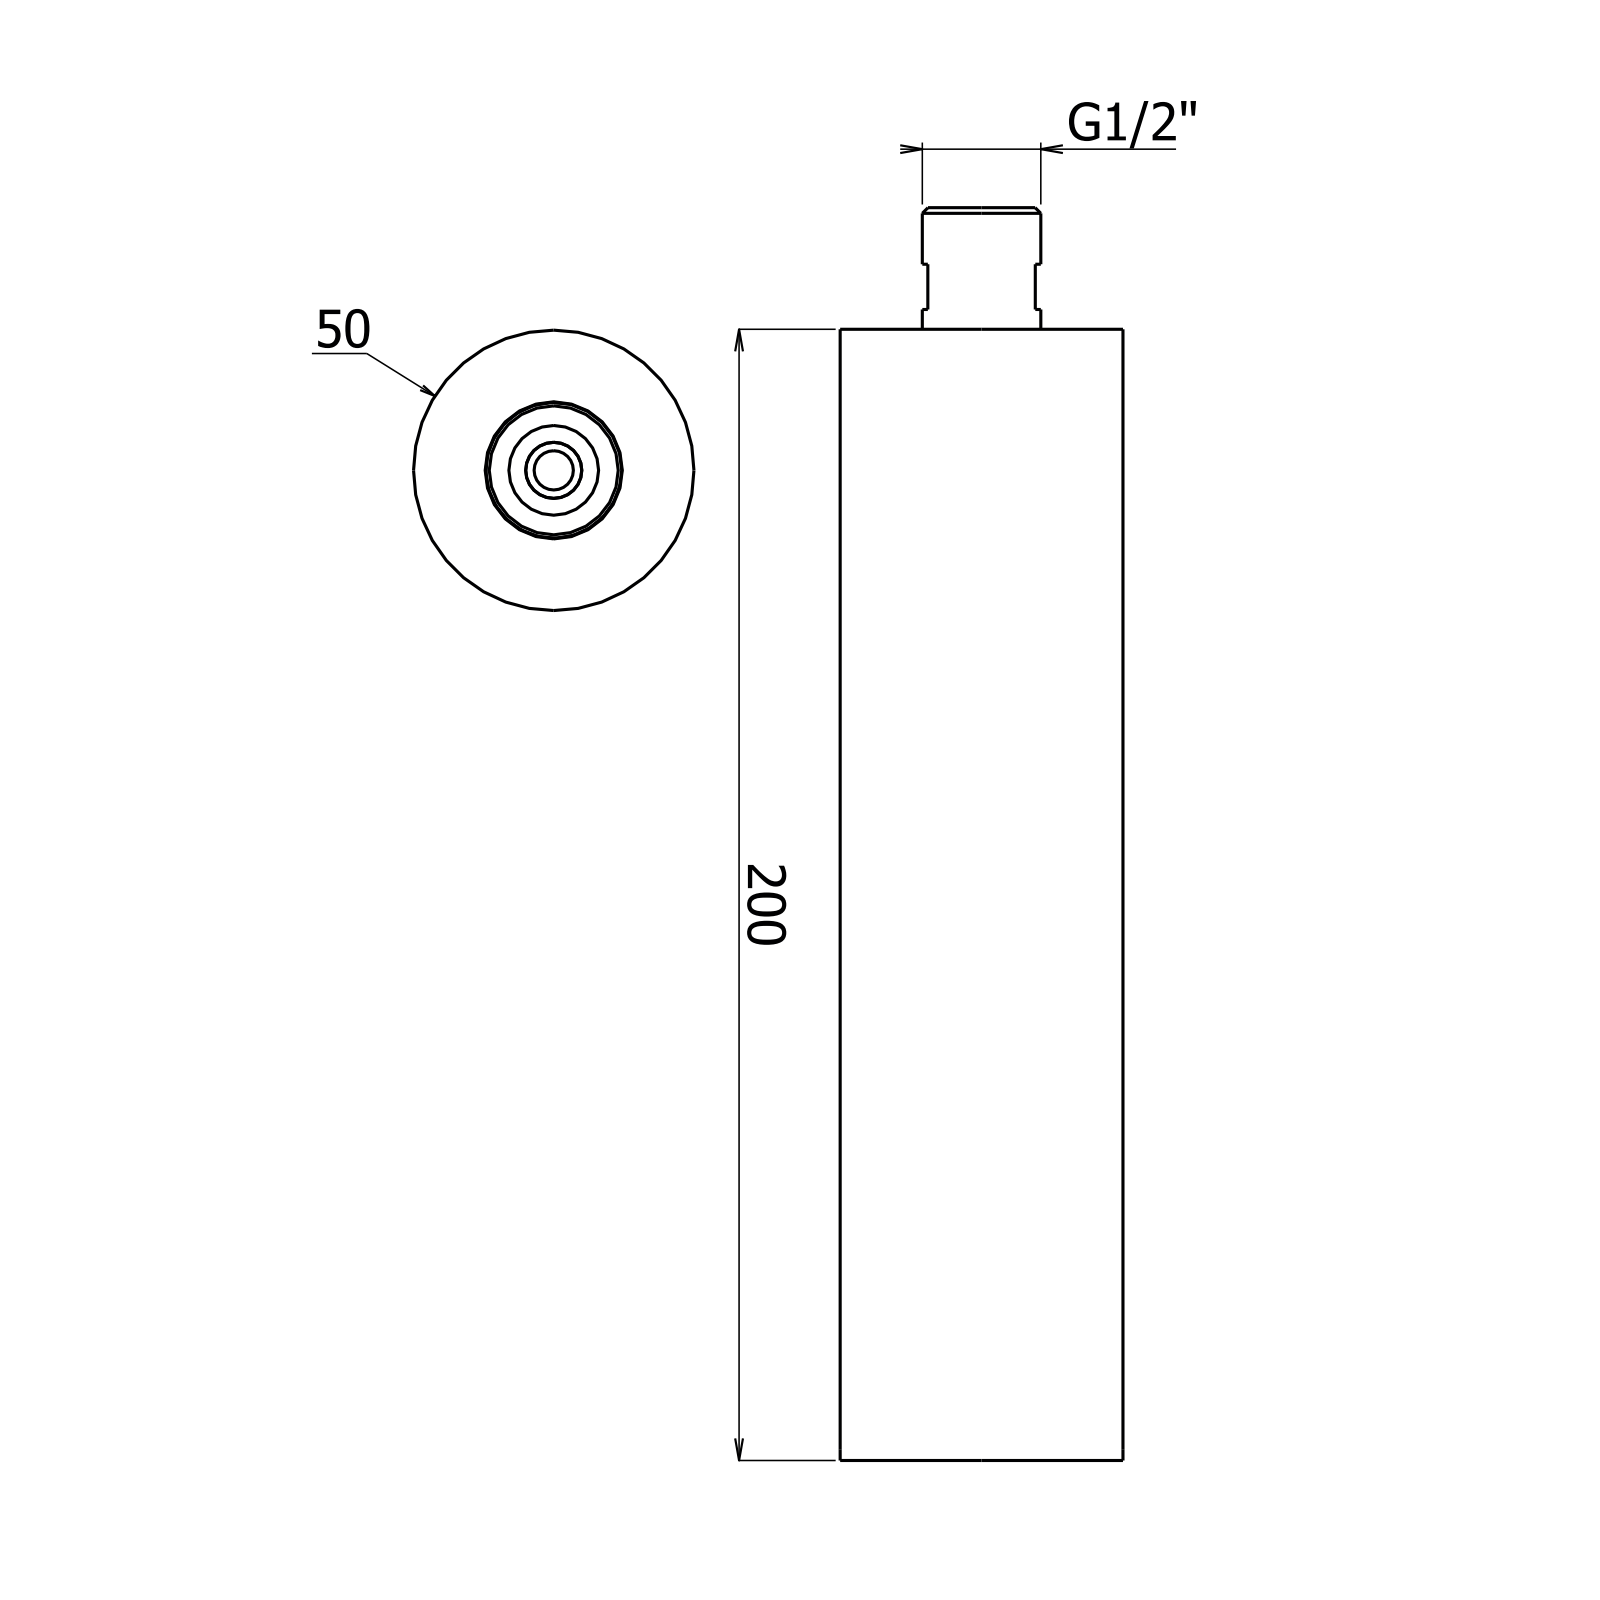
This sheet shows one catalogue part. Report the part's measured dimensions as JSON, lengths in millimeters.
{"part_name": "A.R._24534/20220905", "step_written_by": "Spatial InterOp 3D (AUTOMOTIVE_DESIGN)", "units": "millimeters", "bodies": {"solids": 1, "faces": 3921, "planar": 2829, "cylindrical": 353, "other": 739}, "overall_size": [222.8, 50, 50], "volume_mm3": 99680, "surface_area_mm2": 88324, "round_holes": [[0.8, 2], [1.4, 1], [7.2, 1], [14, 1], [15, 1], [15.6, 1], [16, 1], [16.4, 1], [17.8, 1], [18.63, 1], [23, 1], [24.2, 1]], "round_bosses_or_shafts": [[0.75, 6], [0.8, 4], [26, 1], [24, 1], [23.88, 1], [22.66, 1], [22.55, 1], [21.95, 1]], "partial_cylinders_radius": [[0.15, 66], [0.25, 66], [0.89, 66], [0.84, 50], [0.14, 17], [0.14, 15], [23.39, 4], [23.49, 4]], "face_to_face_distances": [179, 200, 21, 1, 178, 199, 8.5, 18, 17, 161], "hole_center_spacings": [4.82, 9.65]}
